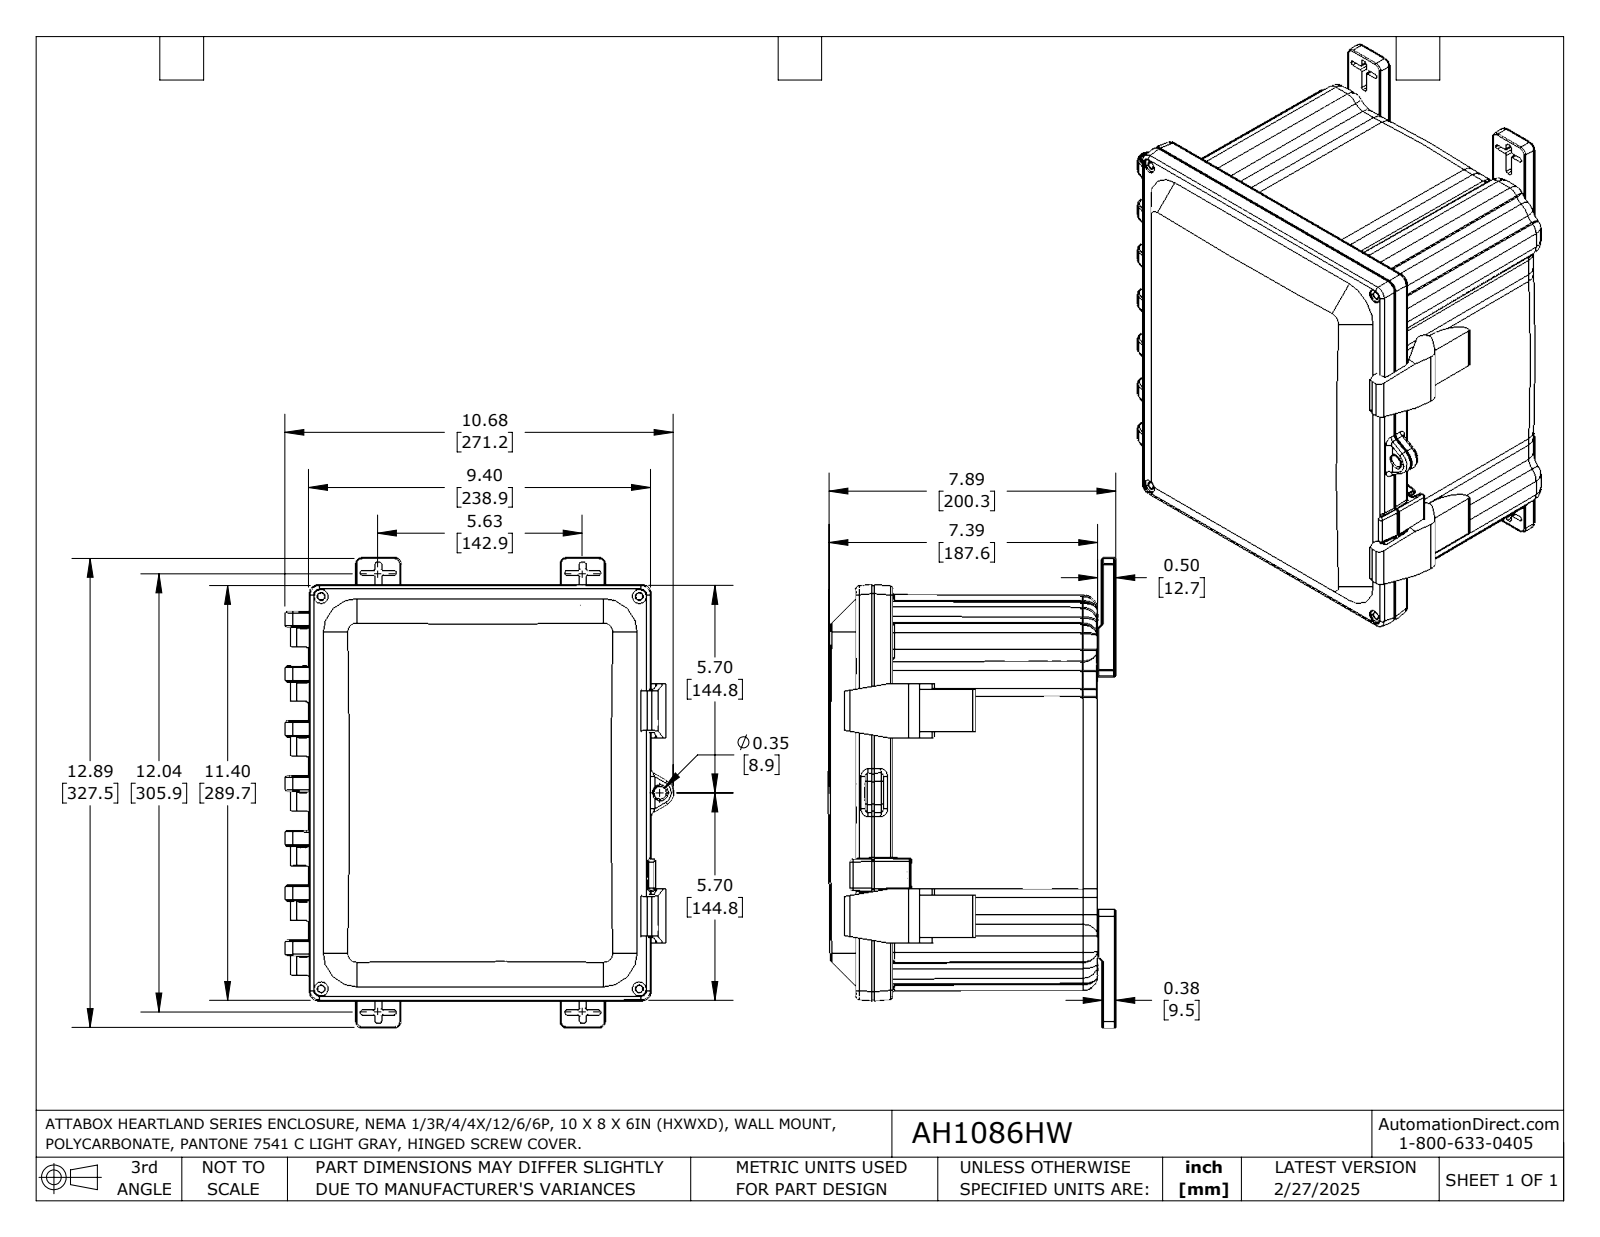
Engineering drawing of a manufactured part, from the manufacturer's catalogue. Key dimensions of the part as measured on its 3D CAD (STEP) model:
Part name (STEP PRODUCT): AH1086HW
STEP written by: SolidWorks 2024 (AUTOMOTIVE_DESIGN)
Units: inches
Bodies: 6 solids, 2339 faces (641 planar, 750 cylindrical, 948 other)
Overall size (bounding box): 12.892 × 10.676 × 7.888
Volume: 98.03 in³ · Surface area: 1 089 in²
Round holes (diameter × count): ⌀0.156 ×4, ⌀0.195 ×4, ⌀0.265 ×4, ⌀0.313 ×4, ⌀0.39 ×4, ⌀0.327 ×1, ⌀0.375 ×1, ⌀0.45 ×1
Round bosses / shafts (diameter × count): ⌀0.25 ×4, ⌀0.313 ×1
Partial cylindrical surfaces — rounded edges, fillets, slot ends (radius × count): R0.05 ×116, R0.035 ×100, R0.065 ×81, R0.02 ×32, R0.03 ×30, R0.025 ×26, R0.01 ×25, R0.18 ×16
Main face-to-face distances: 0.14, 6.14, 6, 0.5, 6.64, 0.133, 0.43, 5.64, 5.5, 0.64
Hole centre spacings: 0.012, 0.442, 5.625, 7.604, 7.633, 7.944, 2.209, 0.43
